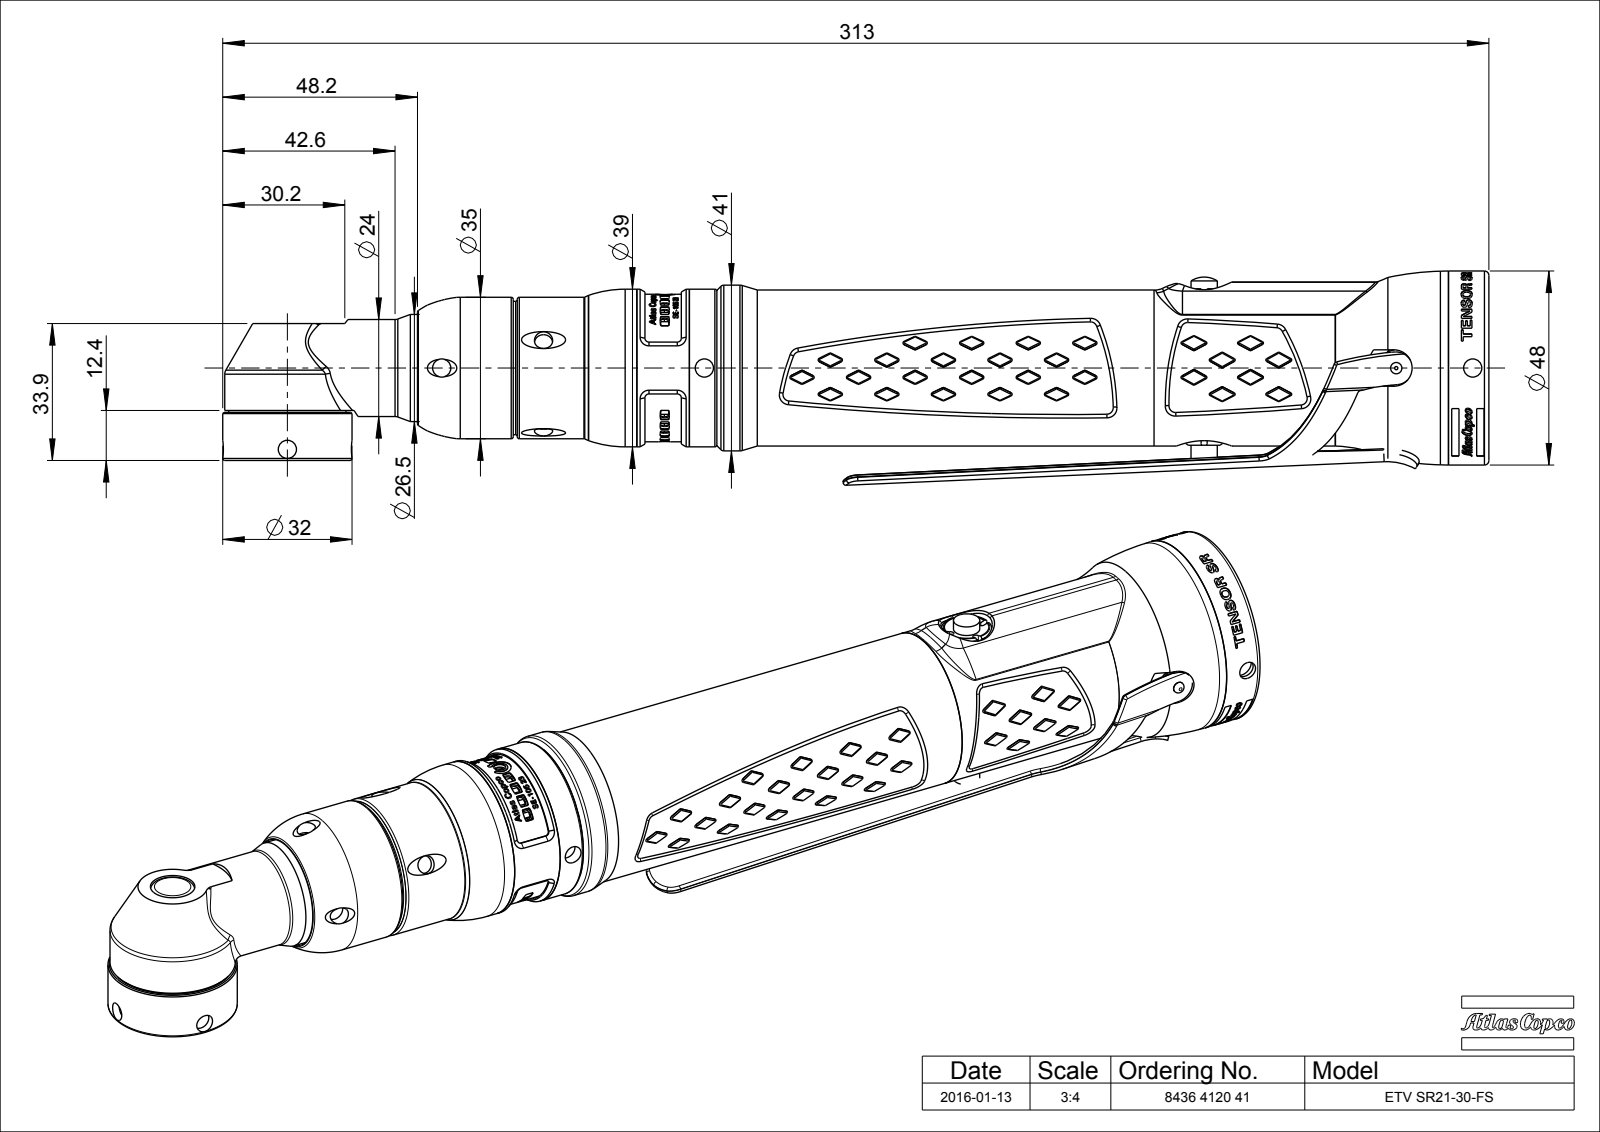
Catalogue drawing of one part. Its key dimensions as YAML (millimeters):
part_name: "4220410004; 4220502200; 4220405381_ASM; 4220406381_ASM (+8 more)"
step_written_by: "CREO PARAMETRIC BY PTC INC, 2015080 (CONFIG_CONTROL_DESIGN)"
units: millimeters
bodies: {solids: 49, faces: 4928, planar: 1696, cylindrical: 998, other: 2234}
overall_size: [313.37, 53, 48]
volume: 117700
surface_area: 136759
round_holes:
  - {diameter: 3.27, count: 12}
  - {diameter: 2.64, count: 11}
  - {diameter: 3.6, count: 11}
  - {diameter: 3.2, count: 9}
  - {diameter: 4.5, count: 9}
  - {diameter: 1, count: 8}
  - {diameter: 0.6, count: 4}
  - {diameter: 2.6, count: 4}
  - {diameter: 1.72, count: 3}
  - {diameter: 7, count: 3}
  - {diameter: 1.5, count: 2}
  - {diameter: 2.5, count: 2}
round_bosses_or_shafts:
  - {diameter: 4, count: 4}
  - {diameter: 3.06, count: 4}
  - {diameter: 2.55, count: 4}
  - {diameter: 2.45, count: 4}
  - {diameter: 2.25, count: 4}
  - {diameter: 1.56, count: 4}
  - {diameter: 4.6, count: 3}
  - {diameter: 2.31, count: 3}
partial_cylinders:
  - {radius: 0.5, count: 82}
  - {radius: 0.2, count: 32}
  - {radius: 0.4, count: 32}
  - {radius: 1, count: 20}
  - {radius: 2, count: 9}
  - {radius: 0.45, count: 8}
  - {radius: 0.75, count: 8}
  - {radius: 1.12, count: 8}
face_to_face_distances: [2.5, 1, 168, 1.2, 23.07, 165.5, 108.2, 57.3, 59.8, 1.5]
hole_center_spacings: [1.5, 2.6, 4.48, 5.56, 15, 21.21, 3, 4.4]
